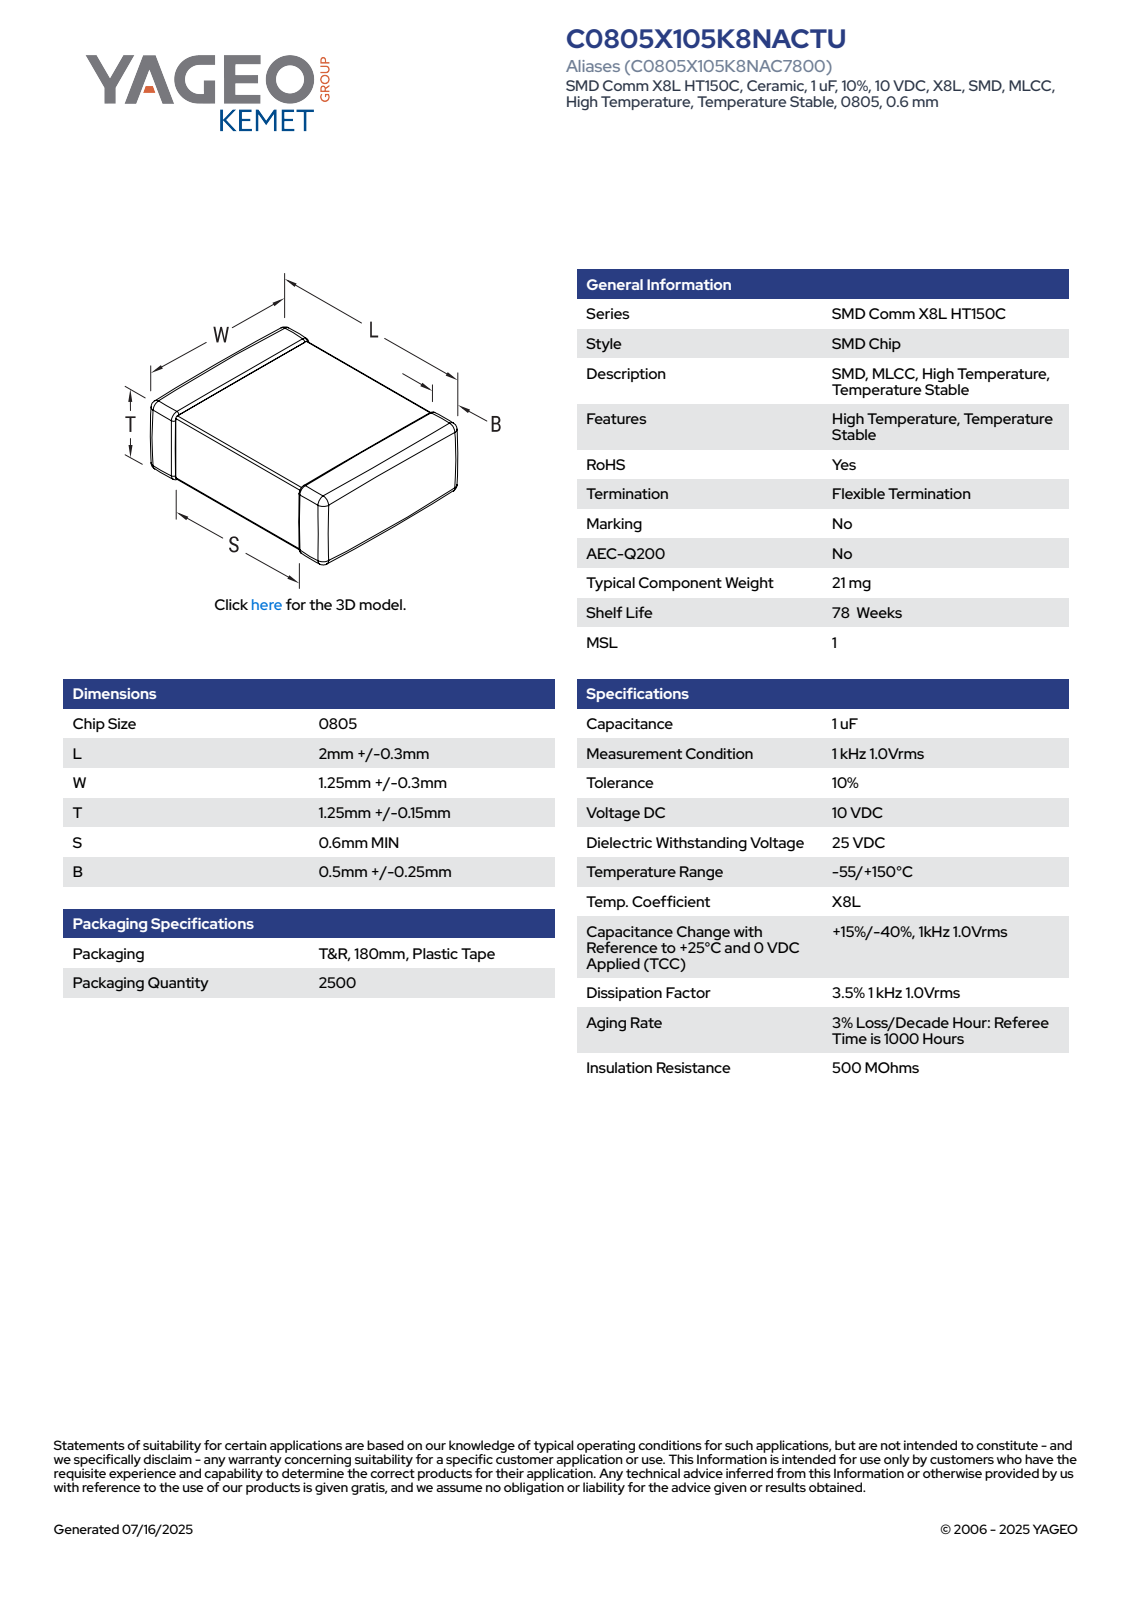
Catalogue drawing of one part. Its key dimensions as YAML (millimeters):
part_name: "CCS_CCSTD_0805_L2.3W1.55S1.25T1.4B0.5"
step_written_by: "SolidWorks 2021 (AUTOMOTIVE_DESIGN)"
units: millimeters
bodies: {solids: 4, faces: 125, planar: 71, cylindrical: 38, other: 16}
overall_size: [2.3, 1.55, 1.4]
volume: 5
surface_area: 18
face_to_face_distances: [1.37, 1.4, 1.52, 2.3, 1.55, 1.34, 1.49, 1.06, 1.24, 1.01]
